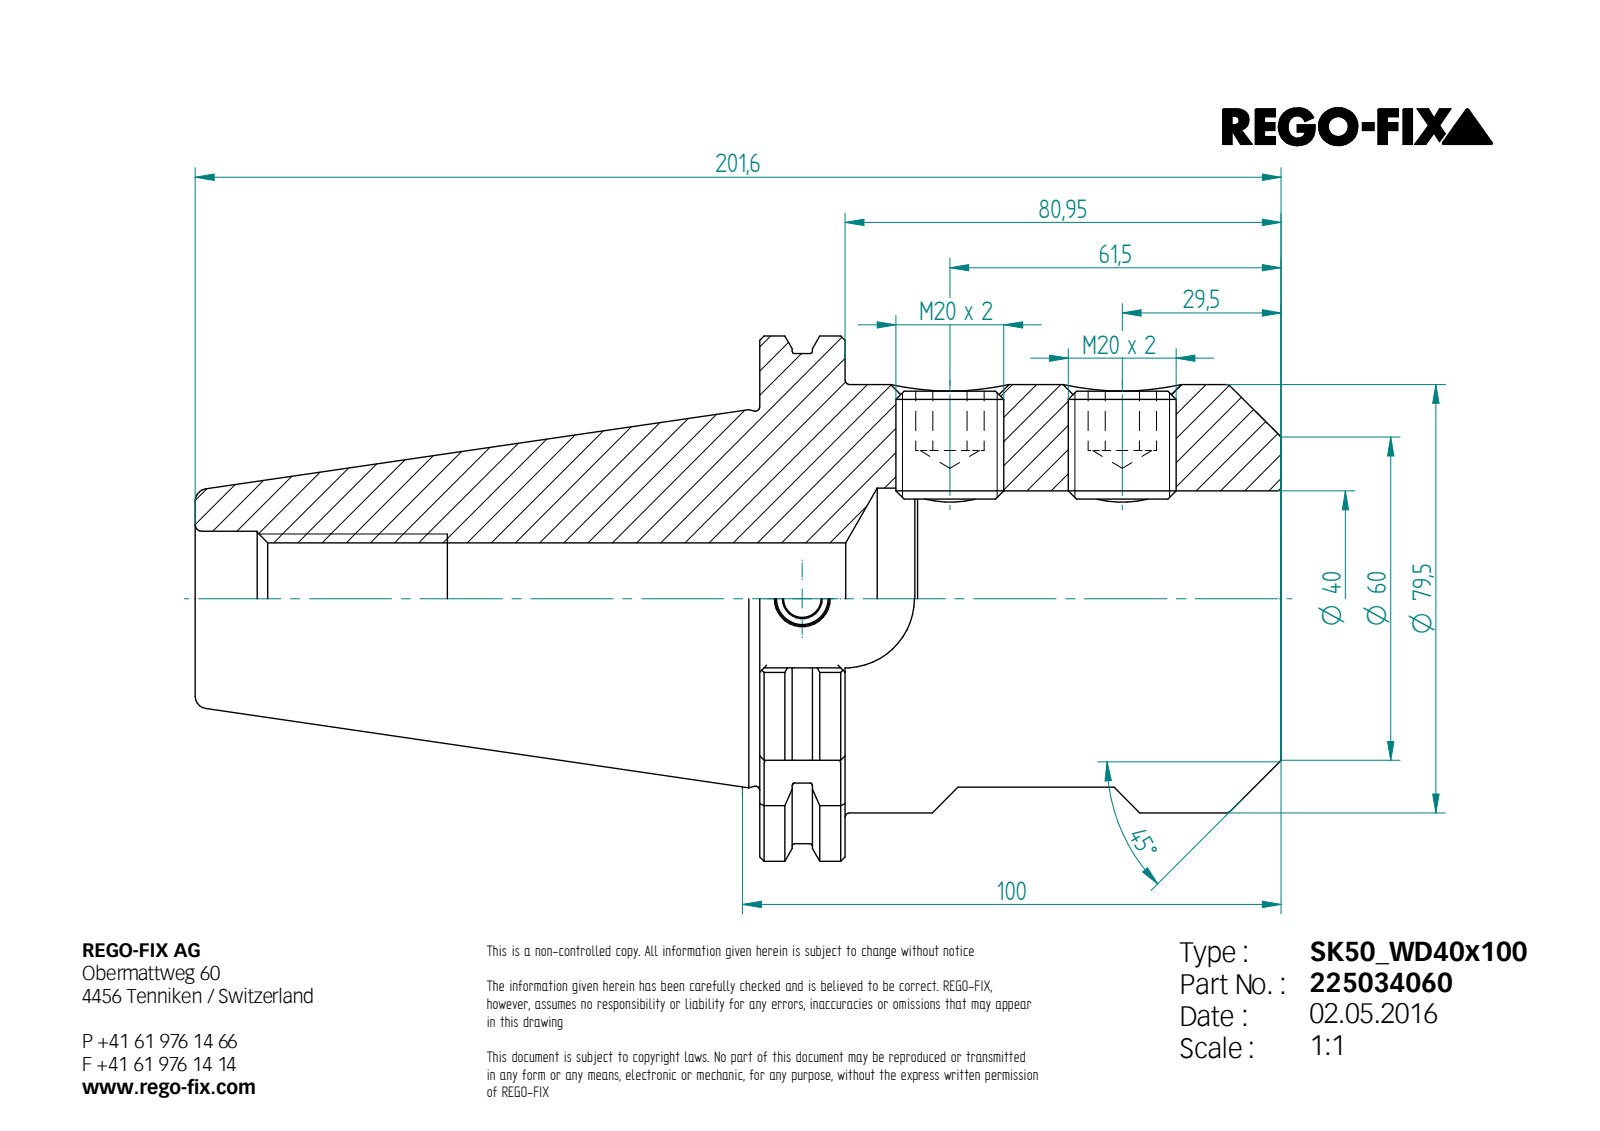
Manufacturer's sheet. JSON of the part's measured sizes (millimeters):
{"step_written_by": "Unknown (AUTOMOTIVE_DESIGN)", "units": "millimeters", "bodies": {"solids": 3, "faces": 149, "planar": 77, "cylindrical": 28, "other": 44}, "overall_size": [201.6, 97.5, 93.58], "volume_mm3": 606545, "surface_area_mm2": 77146, "round_holes": [[17.84, 2], [7, 1], [10, 1], [20.75, 1], [25, 1], [40, 1], [41, 1]], "round_bosses_or_shafts": [[20, 2], [91, 1], [79.5, 1]], "partial_cylinders_radius": [[0.5, 5], [12.85, 1], [12.92, 1], [48.75, 1]], "face_to_face_distances": [15.85, 96.8, 80.95, 72.8, 53.5, 11, 104.8, 120.65, 201.6, 27.71], "hole_center_spacings": [32]}
